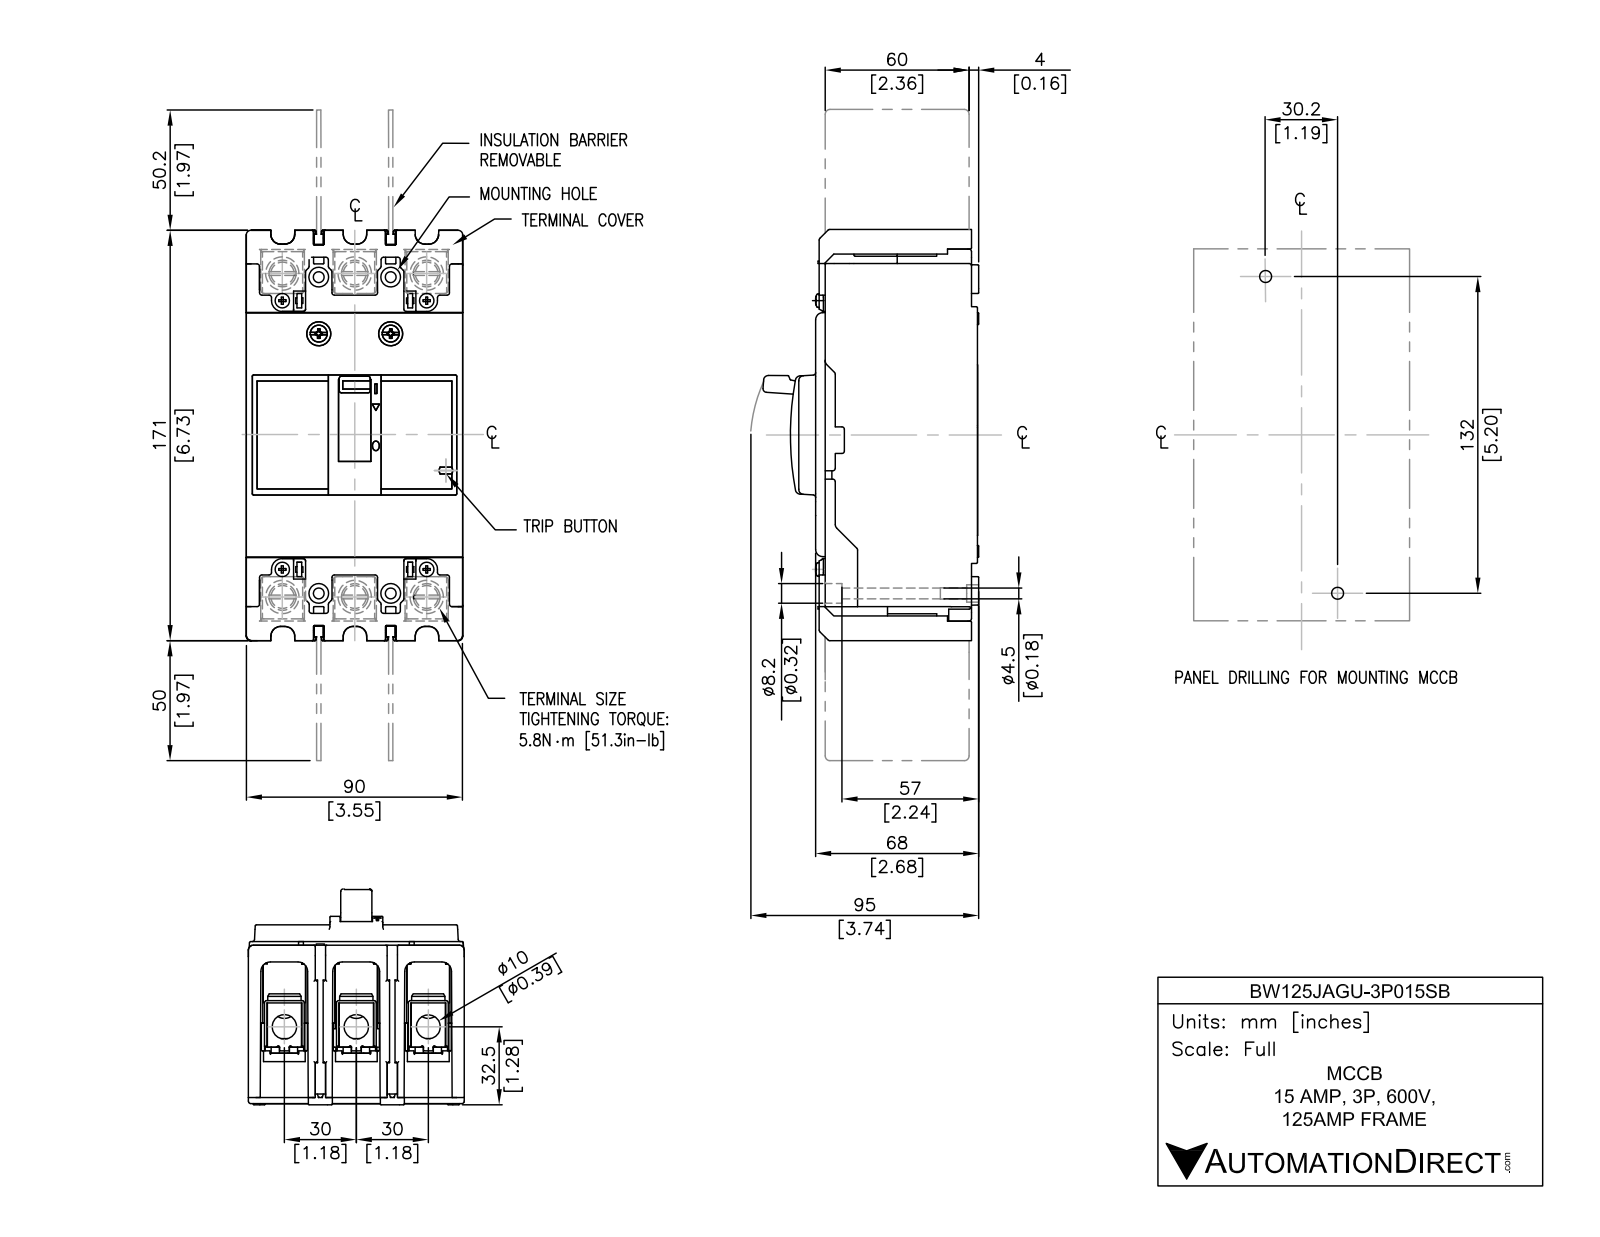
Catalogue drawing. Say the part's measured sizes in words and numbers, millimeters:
The part is named "BW125JAGU-3P015SB". Its 3-D file was written by "SolidWorks 2018 (AUTOMOTIVE_DESIGN)". It is 14 solids with 452 faces: 340 planar, 88 cylindrical and 24 other. Overall it measures 259 by 91.5 by 90 millimeters. Its volume is 940 600 cubic millimeters and its surface area 148 600 square millimeters. Round holes: 6 of diameter 8, 4 of diameter 4.5, 4 of diameter 8.2. Round bosses or shafts: 6 of diameter 12. Partial cylindrical surfaces (rounded edges, fillets, slot ends): 12 of radius 4, 6 of radius 2, 6 of radius 3. The main face-to-face distances are 30, 28.2, 31.8, 58.2, 61.8, 3.6, 90, 6, 61, 26.4. The hole center spacings are 15.1, 134.3, 30, 45, 138.3, 140.9, 135, 60.
